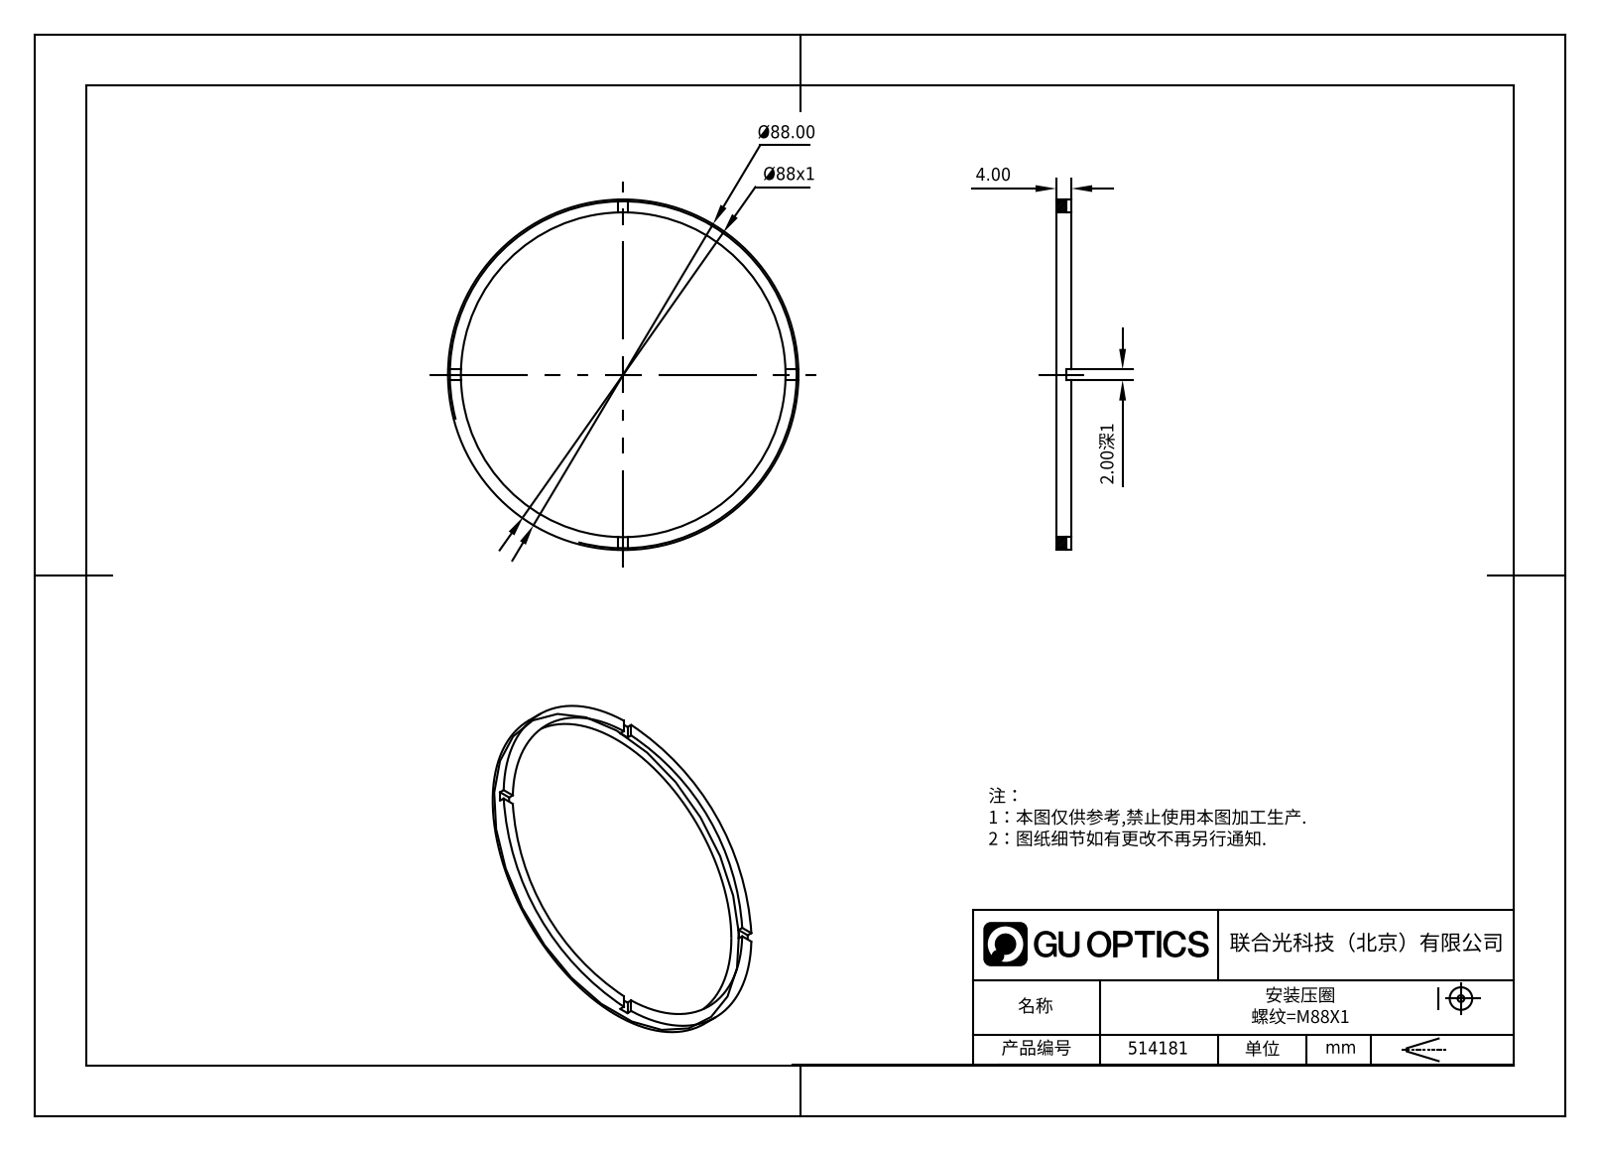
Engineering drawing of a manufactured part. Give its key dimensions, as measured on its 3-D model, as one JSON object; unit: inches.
{"part_name": "514181", "step_written_by": "SolidWorks 2020 (CONFIG_CONTROL_DESIGN)", "units": "inches", "bodies": {"solids": 1, "faces": 21, "planar": 17, "cylindrical": 4, "other": 0}, "overall_size": [3.465, 3.465, 0.157], "volume_in3": 0.194, "surface_area_in2": 5.806, "round_holes": [[3.228, 1]], "round_bosses_or_shafts": [[3.465, 1]], "face_to_face_distances": [0.157, 0.118, 0.039, 0.079]}
